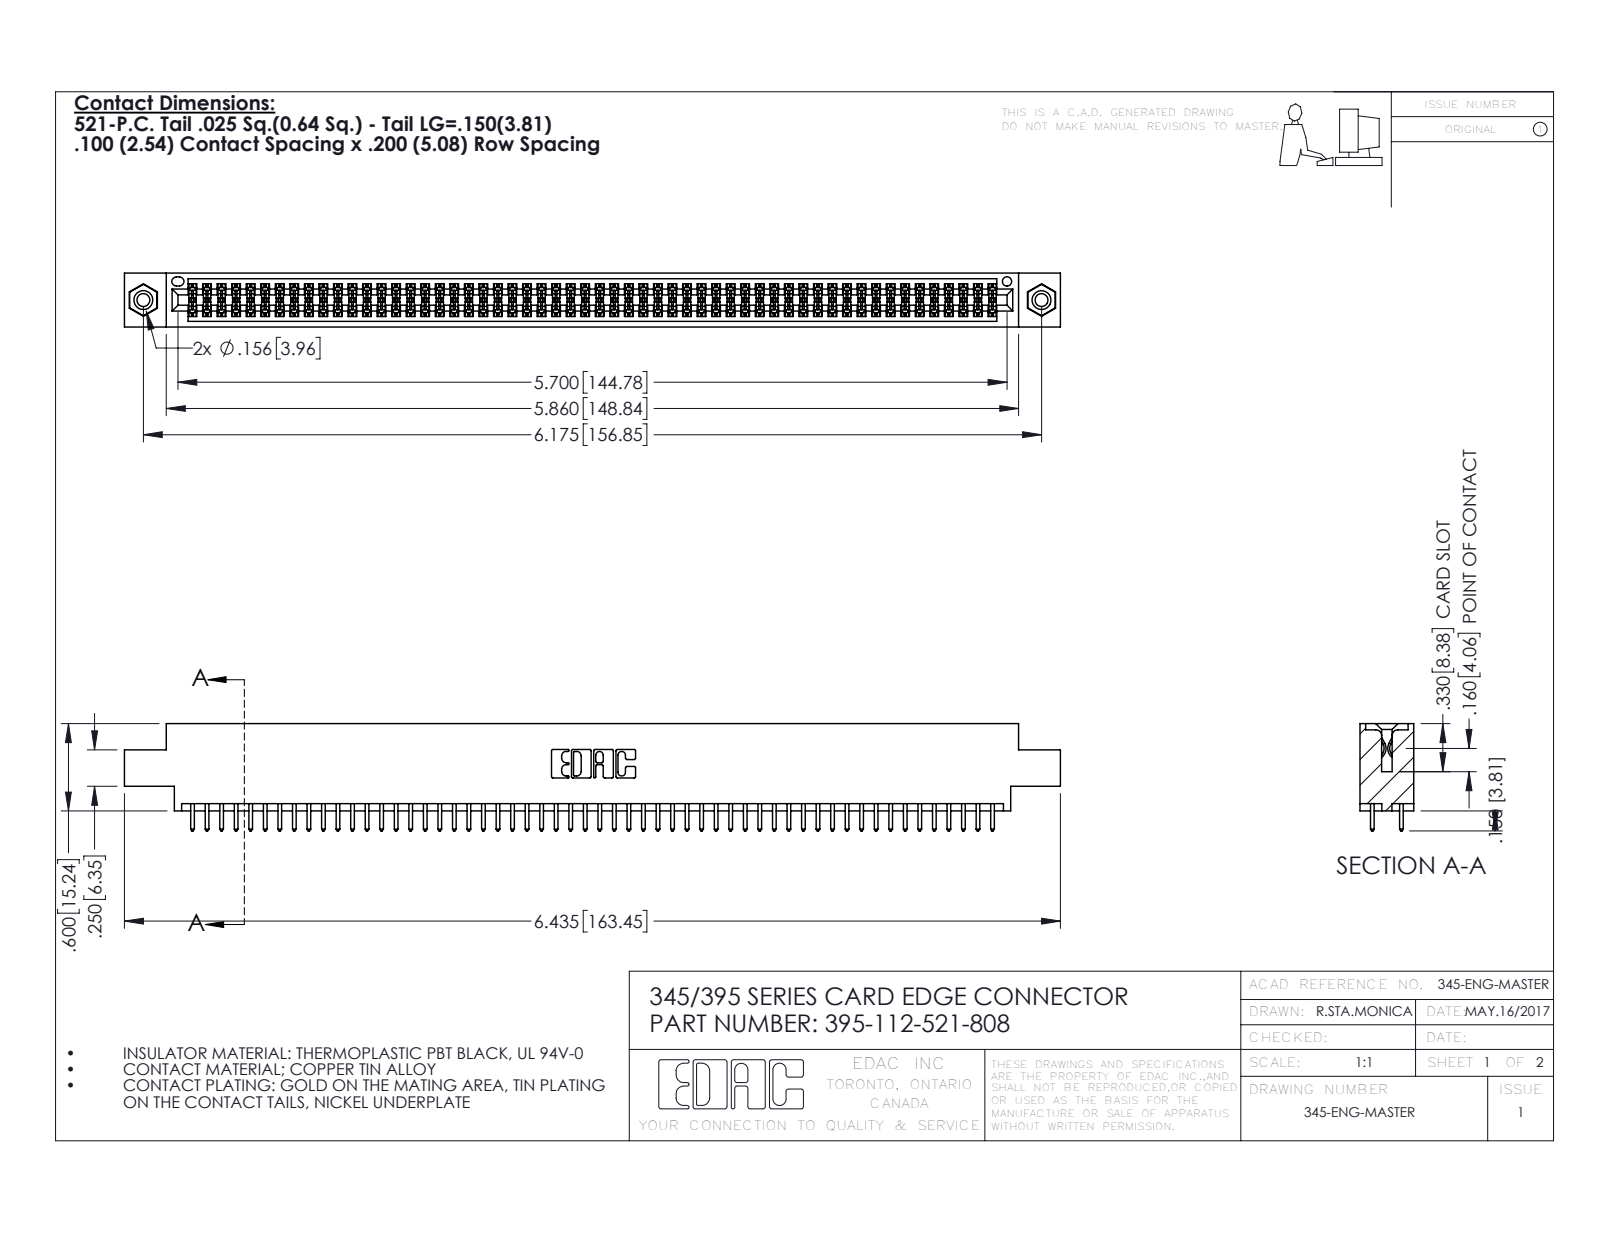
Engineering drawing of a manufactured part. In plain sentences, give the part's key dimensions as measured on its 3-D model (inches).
The part is named "345 Part_0.170 Offset - 0.156 Dia-TI; 345-292-001_345-293-121; 395-112-521-808; 345-250-001_345-250-003-102". Its 3-D file was written by "SolidWorks 2016 (CONFIG_CONTROL_DESIGN)". It is 115 solids with 5790 faces: 3812 planar, 1962 cylindrical and 16 other. Overall it measures 6.435 by 0.737 by 0.37 inches. Its volume is 0.967 cubic inches and its surface area 36.5 square inches. Round holes: 2 of diameter 0.089, 2 of diameter 0.125, 2 of diameter 0.156, 1 of diameter 0.064. Round bosses or shafts: 2 of diameter 0.155. Partial cylindrical surfaces (rounded edges, fillets, slot ends): 168 of radius 0.006, 112 of radius 0.01, 22 of radius 0.01, 6 of radius 0.007, 6 of radius 0.031, 3 of radius 0.026, 2 of radius 0.014, 2 of radius 0.019. The main face-to-face distances are 0.072, 0.298, 0.2, 0.37, 0.098, 0.272, 0.025, 0.225, 0.175, 0.149. The hole center spacings are 0.27, 5.939, 6.175.
